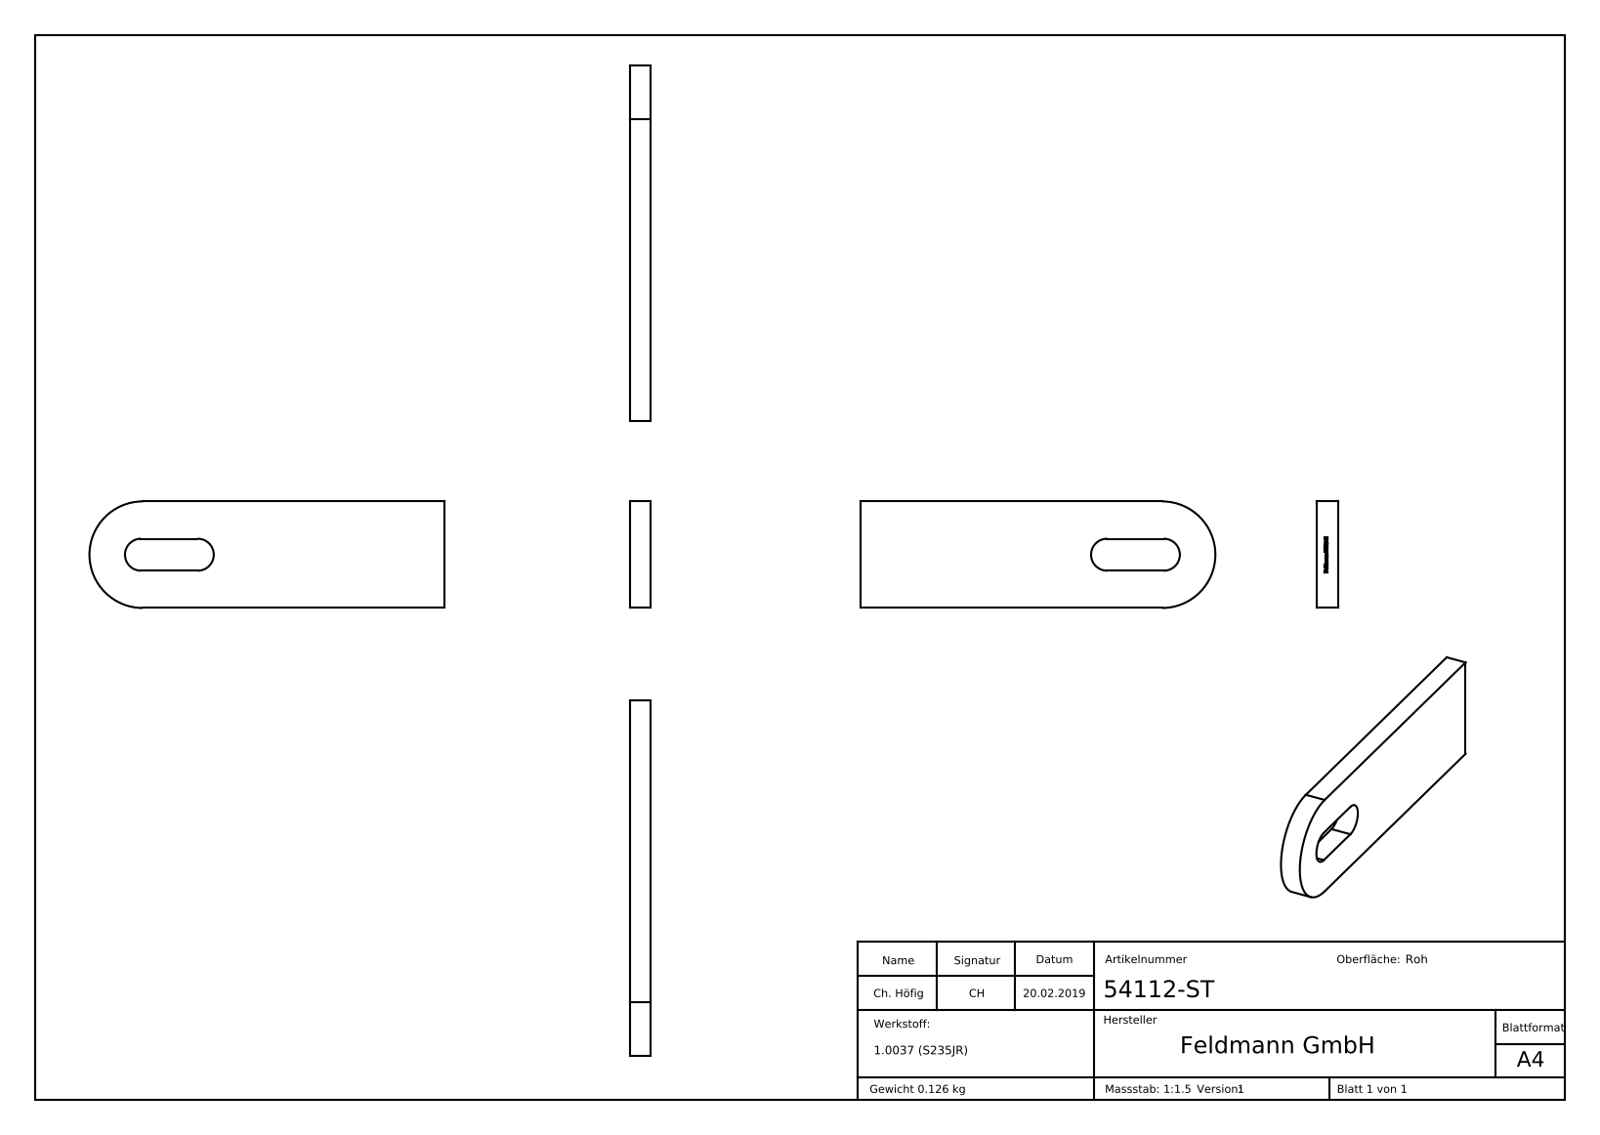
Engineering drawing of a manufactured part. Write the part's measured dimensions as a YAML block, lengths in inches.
part_name: "54112-ST"
step_written_by: "SolidWorks 2015 (CONFIG_CONTROL_DESIGN)"
units: inches
bodies: {solids: 1, faces: 214, planar: 132, cylindrical: 5, other: 77}
overall_size: [3.937, 1.181, 0.236]
volume: 0.987
surface_area: 11.22
partial_cylinders:
  - {radius: 0.177, count: 2}
  - {radius: 0.591, count: 1}
face_to_face_distances: [0.236, 1.181, 0.413, 0.768, 0.354, 0.118, 0.024, 0.028, 0.23, 0.254]
